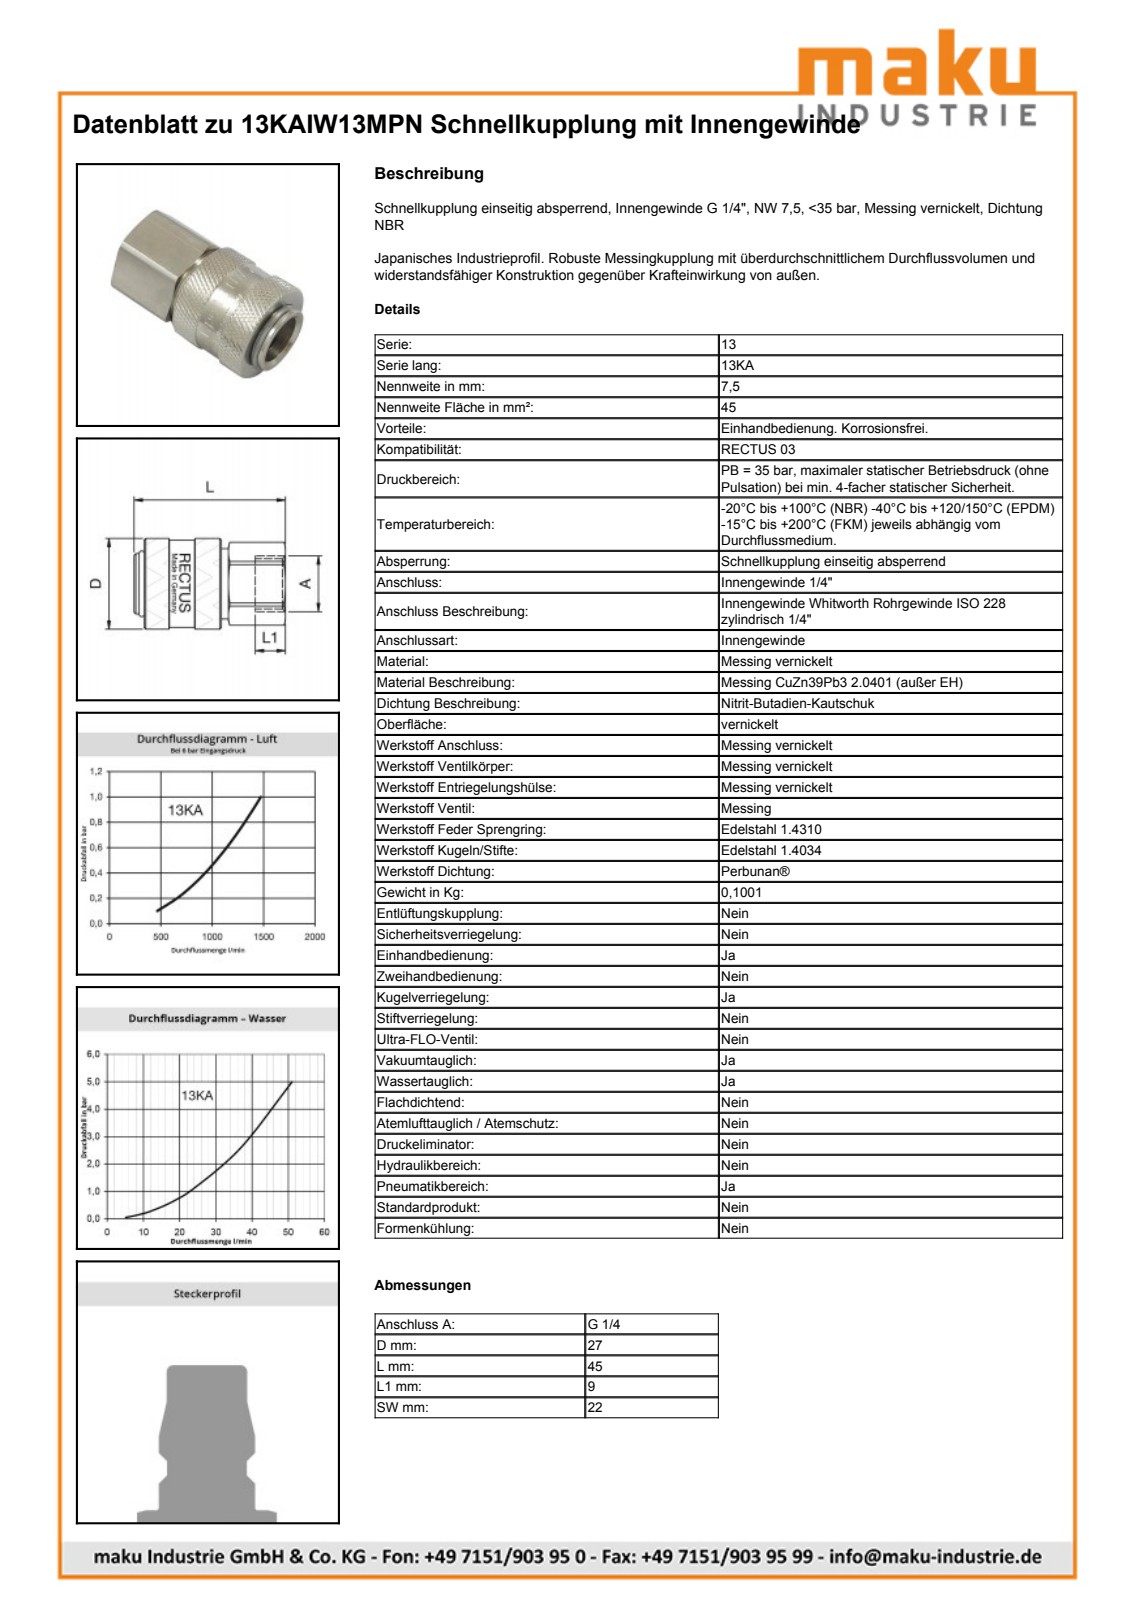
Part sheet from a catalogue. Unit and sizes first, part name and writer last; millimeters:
Units: millimetres
Overall size (bounding box): 45.1 × 27.15 × 27.15
Round holes (diameter × count): ⌀11.45 ×1, ⌀14.45 ×1, ⌀15.75 ×1, ⌀17 ×1, ⌀18 ×1, ⌀21 ×1, ⌀24.6 ×1
Round bosses / shafts (diameter × count): ⌀27.15 ×1, ⌀26 ×1, ⌀16.65 ×1, ⌀15.61 ×1
Partial cylindrical surfaces — rounded edges, fillets, slot ends (radius × count): R12.35 ×1, R12.9 ×1
Main face-to-face distances: 22, 42.1, 3, 45.1, 23.05, 26.05, 19.05, 21.98, 1.5, 33.99
Volume: 15 810 mm³ · Surface area: 9 410 mm²
Bodies: 2 solids, 564 faces (231 planar, 69 cylindrical, 264 other)
Part name (STEP PRODUCT): D112775
STEP written by: Autodesk Inventor 2013 (AUTOMOTIVE_DESIGN)
